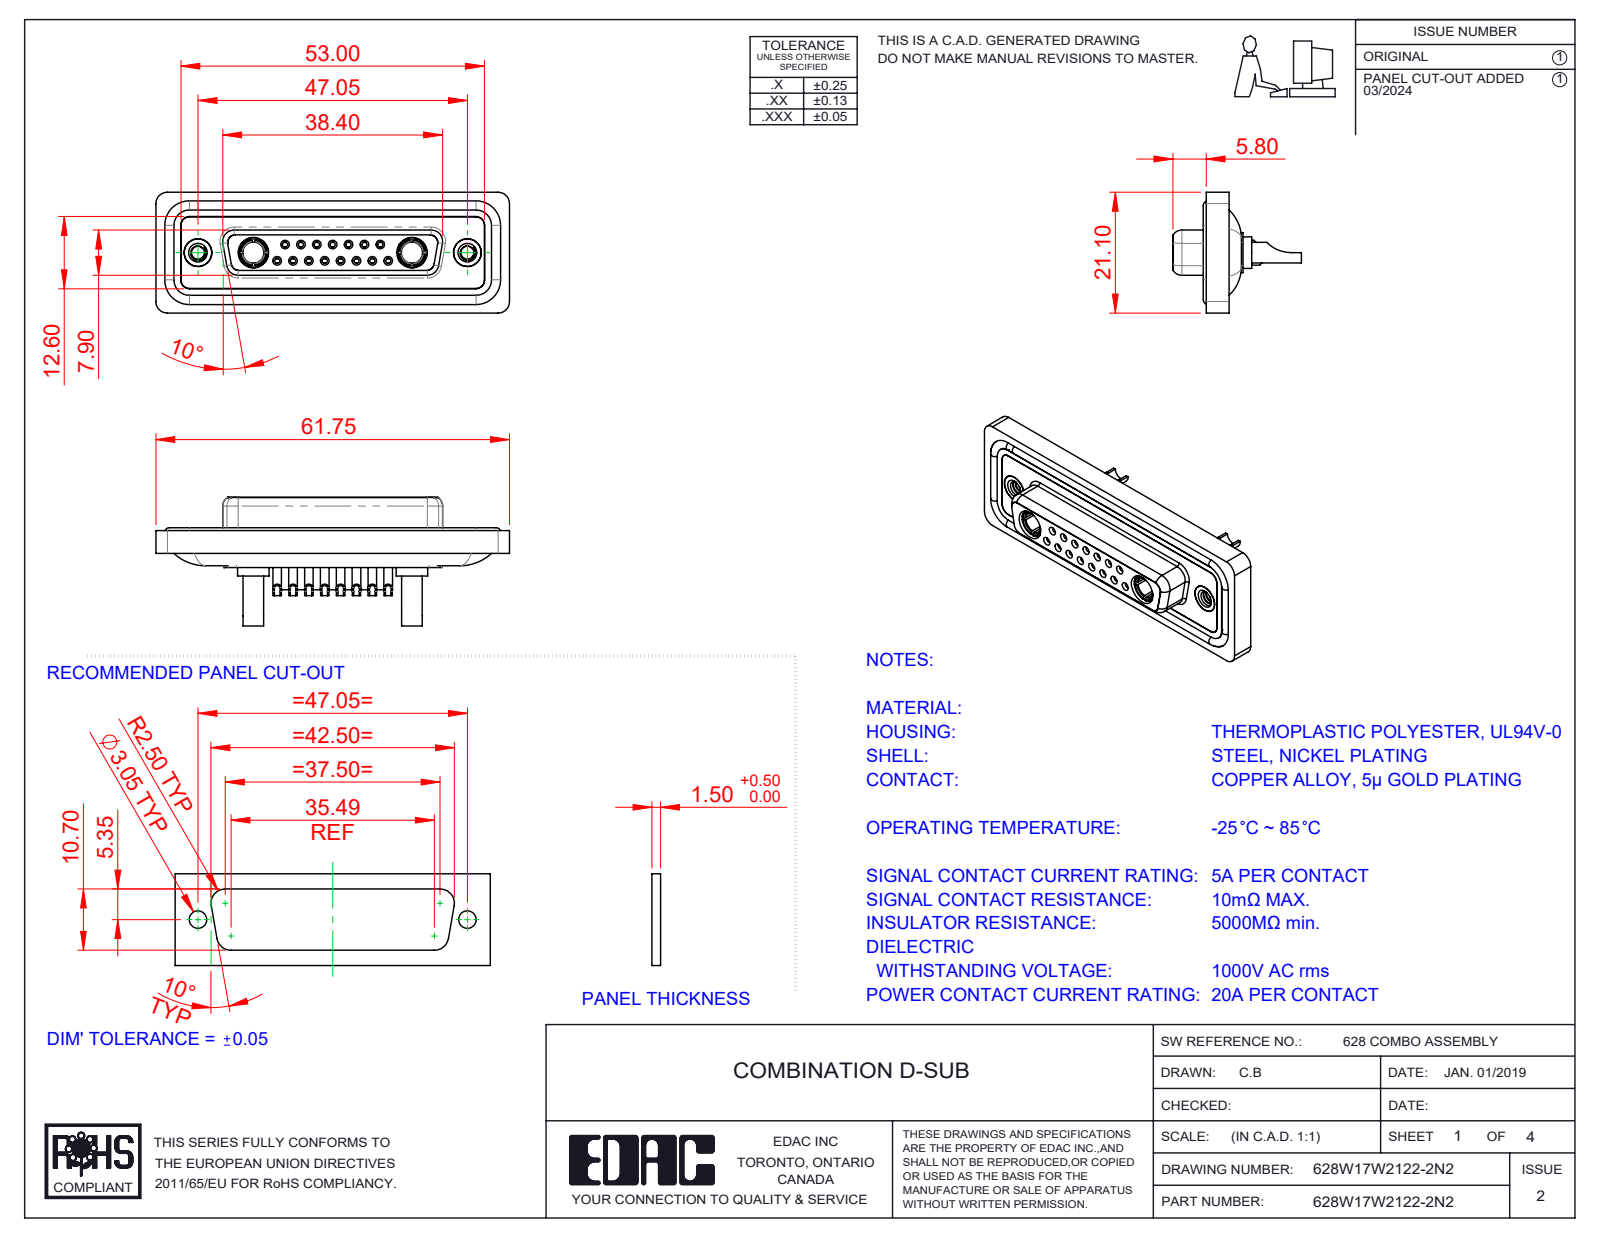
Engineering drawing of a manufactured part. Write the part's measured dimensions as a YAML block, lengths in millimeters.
part_name: "628Combo Threaded Rivet_2; 628Combo Shell Front_25 Contacts; Power Socket_20A SC; 628Combo Housing_17W2 (+5 more)"
step_written_by: "SolidWorks 2023 (CONFIG_CONTROL_DESIGN)"
units: millimeters
bodies: {solids: 26, faces: 1371, planar: 424, cylindrical: 555, other: 392}
overall_size: [61.75, 22.45, 21.1]
volume: 8381
surface_area: 14180
round_holes:
  - {diameter: 0.9, count: 15}
  - {diameter: 1, count: 15}
  - {diameter: 1.1, count: 15}
  - {diameter: 1.5, count: 15}
  - {diameter: 2, count: 15}
  - {diameter: 1.6, count: 8}
  - {diameter: 1.7, count: 7}
  - {diameter: 4.85, count: 4}
  - {diameter: 2.26, count: 2}
  - {diameter: 2.7, count: 2}
  - {diameter: 3.7, count: 2}
  - {diameter: 4, count: 2}
round_bosses_or_shafts:
  - {diameter: 2.2, count: 15}
  - {diameter: 1.6, count: 11}
  - {diameter: 5.5, count: 2}
  - {diameter: 5.2, count: 2}
  - {diameter: 4.96, count: 2}
  - {diameter: 4.95, count: 2}
  - {diameter: 4.8, count: 2}
  - {diameter: 4.75, count: 2}
partial_cylinders:
  - {radius: 1.5, count: 22}
  - {radius: 2, count: 18}
  - {radius: 1.35, count: 8}
  - {radius: 1.6, count: 8}
  - {radius: 1, count: 6}
  - {radius: 0.25, count: 4}
  - {radius: 0.5, count: 4}
  - {radius: 0.6, count: 4}
face_to_face_distances: [0.4, 1.8, 7.45, 5.65, 6.6, 0.5, 7.05, 1.6, 2.9, 1.1]
hole_center_spacings: [3.16, 2.77, 8.31, 5.54, 5.03, 5.04, 7.49, 11.08]
